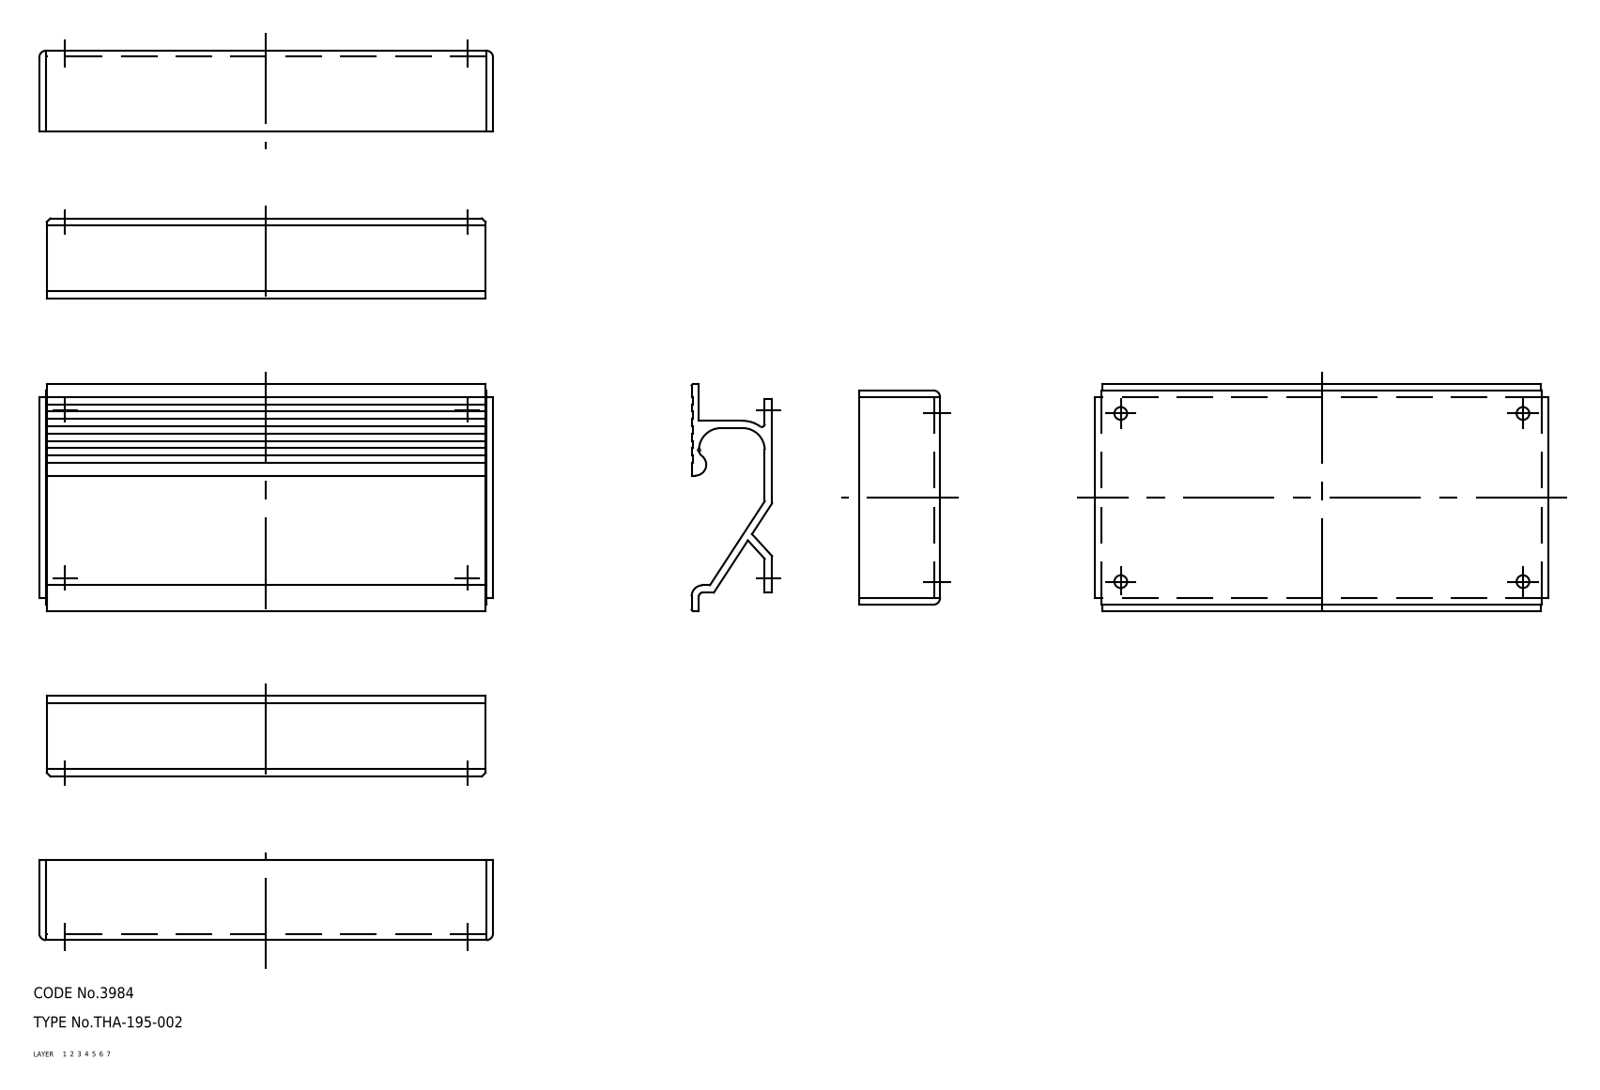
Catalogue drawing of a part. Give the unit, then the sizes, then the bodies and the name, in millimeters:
Units: millimetres
Overall size (bounding box): 124.1 × 62 × 24.2
Volume: 56 351 mm³ · Surface area: 60 811 mm²
Bodies: 2 solids, 101 faces (0 planar, 0 cylindrical, 101 other)
Part name (STEP PRODUCT): pull; bracket; THA_195_002_2846_36
STEP written by: CADfix (AUTOMOTIVE_DESIGN)
